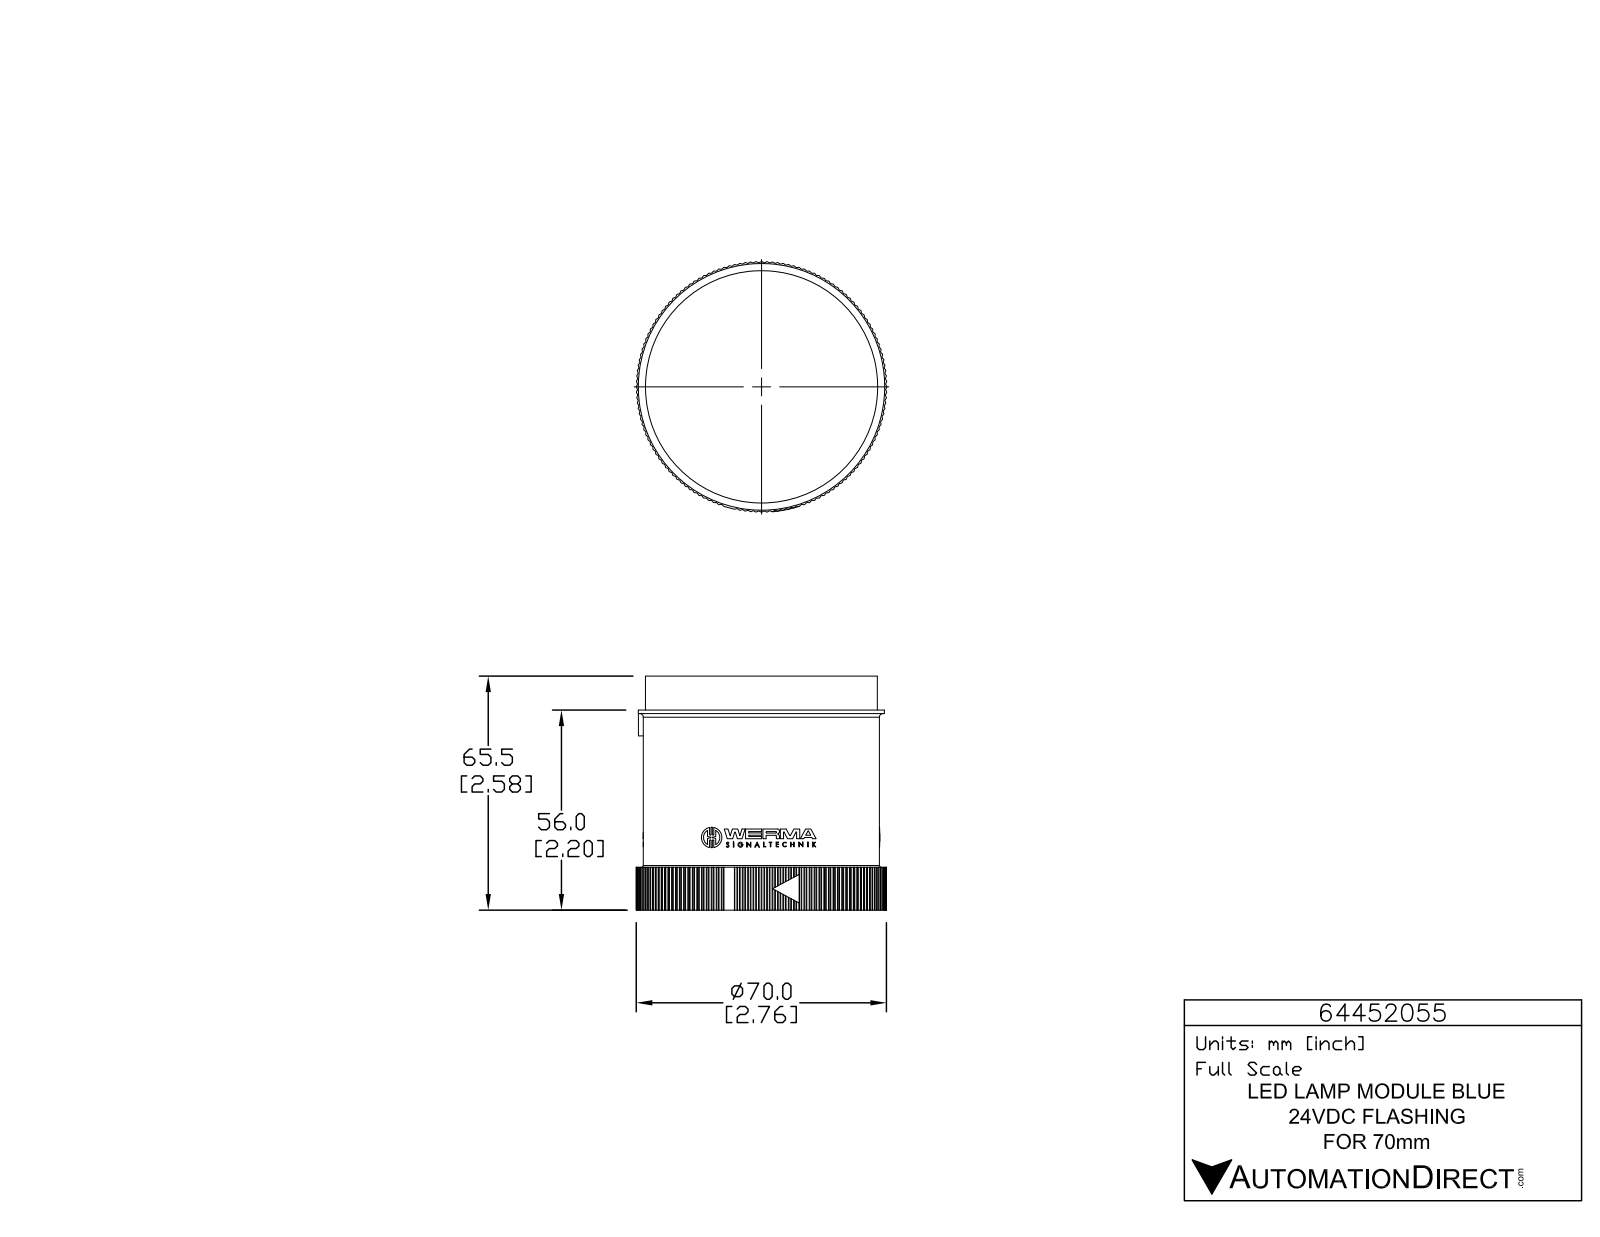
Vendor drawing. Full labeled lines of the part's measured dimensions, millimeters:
Part name (STEP PRODUCT): 64452055
STEP written by: SolidWorks 2015 (AUTOMOTIVE_DESIGN)
Units: millimetres
Bodies: 1 solid, 1400 faces (832 planar, 563 cylindrical, 5 other)
Overall size (bounding box): 70.2 × 70.2 × 65.5
Volume: 197 000 mm³ · Surface area: 24 180 mm²
Round holes (diameter × count): ⌀1 ×3, ⌀65.4 ×1
Round bosses / shafts (diameter × count): ⌀5.7 ×3, ⌀1.4 ×3, ⌀69 ×1, ⌀66.2 ×1, ⌀65 ×1
Partial cylindrical surfaces — rounded edges, fillets, slot ends (radius × count): R0.2 ×285, R0.2 ×6, R0.2 ×6, R0.2 ×6, R3.3 ×6, R0.1 ×3, R0.1 ×3, R0.2 ×3
Main face-to-face distances: 55.9, 62.3, 9.6, 65.5, 56, 46.4, 9.5, 62.3, 12, 2.4
